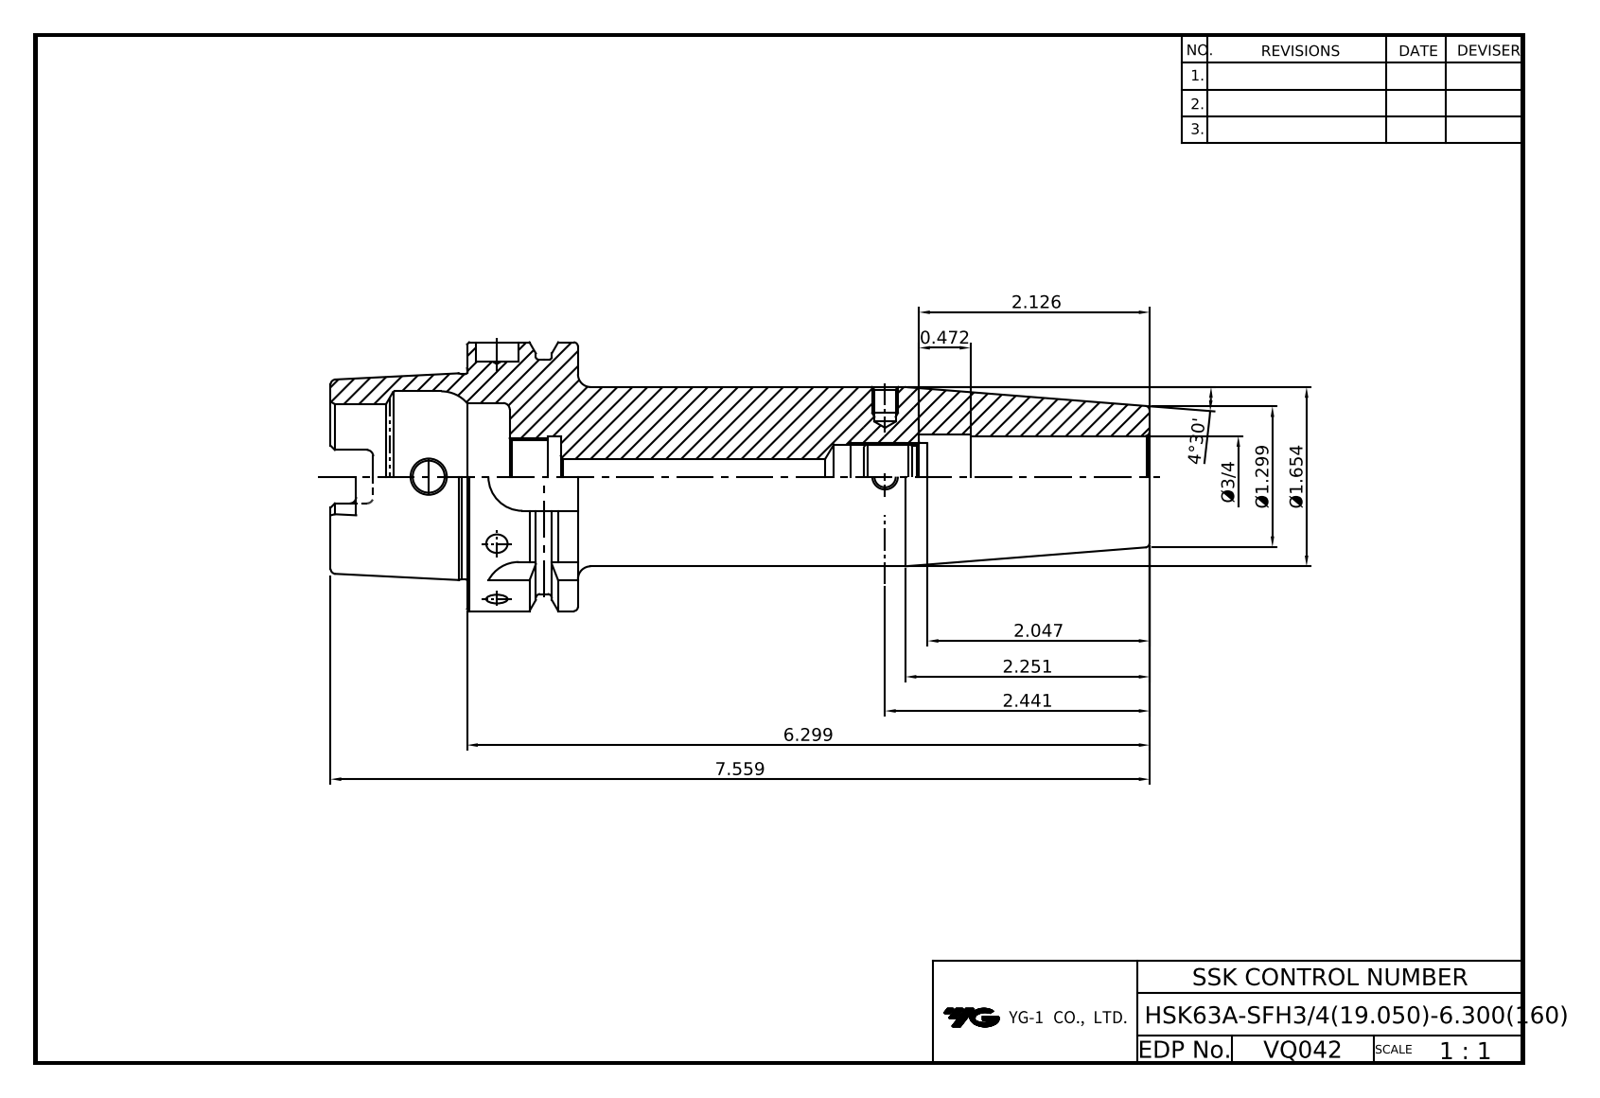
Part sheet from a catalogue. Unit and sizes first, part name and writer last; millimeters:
Units: millimetres
Overall size (bounding box): 192 × 63 × 63
Round holes (diameter × count): ⌀7.5 ×1, ⌀8 ×1, ⌀10 ×1, ⌀14.92 ×1, ⌀16.92 ×1, ⌀19 ×1, ⌀19.05 ×1, ⌀20.25 ×1, ⌀34 ×1, ⌀40 ×1
Round bosses / shafts (diameter × count): ⌀63 ×1, ⌀55 ×1, ⌀48.04 ×1, ⌀42 ×1
Partial cylindrical surfaces — rounded edges, fillets, slot ends (radius × count): R1.5 ×6, R2.88 ×4, R8 ×4
Main face-to-face distances: 26, 10, 16, 150, 160, 134, 32, 42, 54, 138
Volume: 228 760 mm³ · Surface area: 44 272 mm²
Bodies: 1 solid, 116 faces (42 planar, 34 cylindrical, 40 other)
Part name (STEP PRODUCT): LO-HSK63A-SFH19.05-160
STEP written by: Autodesk Inventor 2022 (AUTOMOTIVE_DESIGN)
